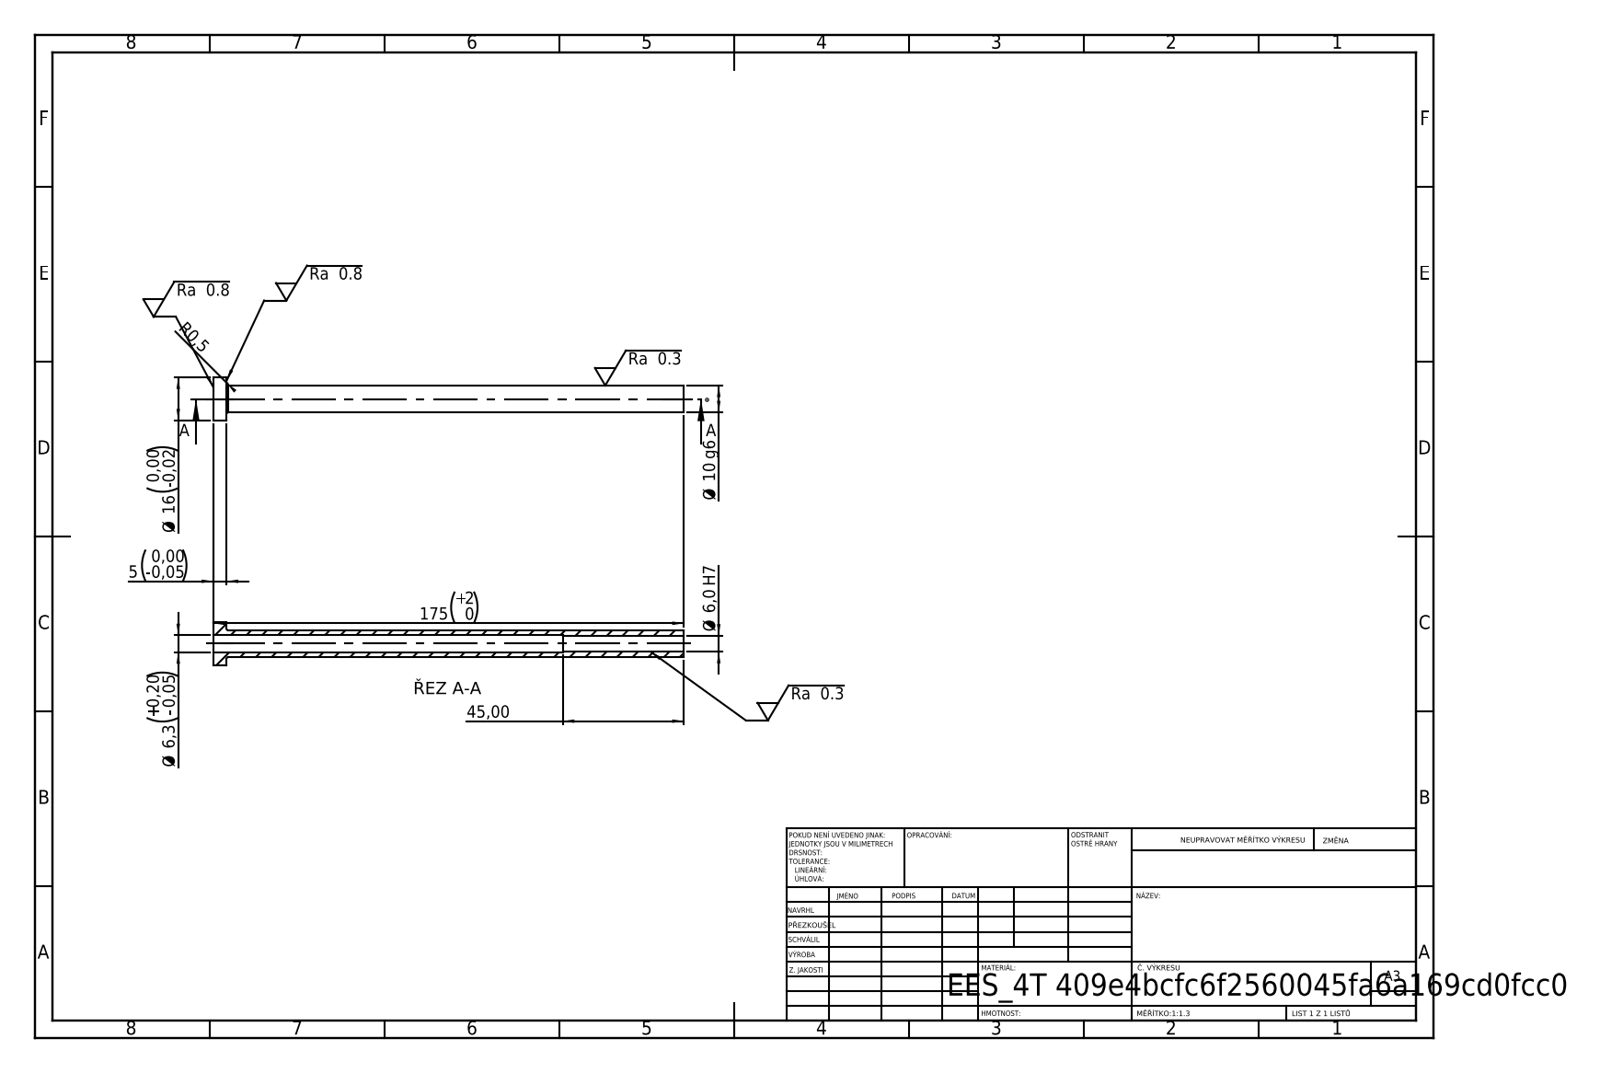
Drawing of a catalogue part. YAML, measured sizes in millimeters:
step_written_by: "SolidWorks 2019 (CONFIG_CONTROL_DESIGN)"
units: millimeters
bodies: {solids: 1, faces: 14, planar: 4, cylindrical: 8, other: 2}
overall_size: [175, 16, 16]
volume: 9034
surface_area: 9352
round_holes:
  - {diameter: 6, count: 1}
  - {diameter: 6.3, count: 1}
round_bosses_or_shafts:
  - {diameter: 16, count: 1}
  - {diameter: 10, count: 1}
face_to_face_distances: [5, 175, 170, 130, 125, 45]
